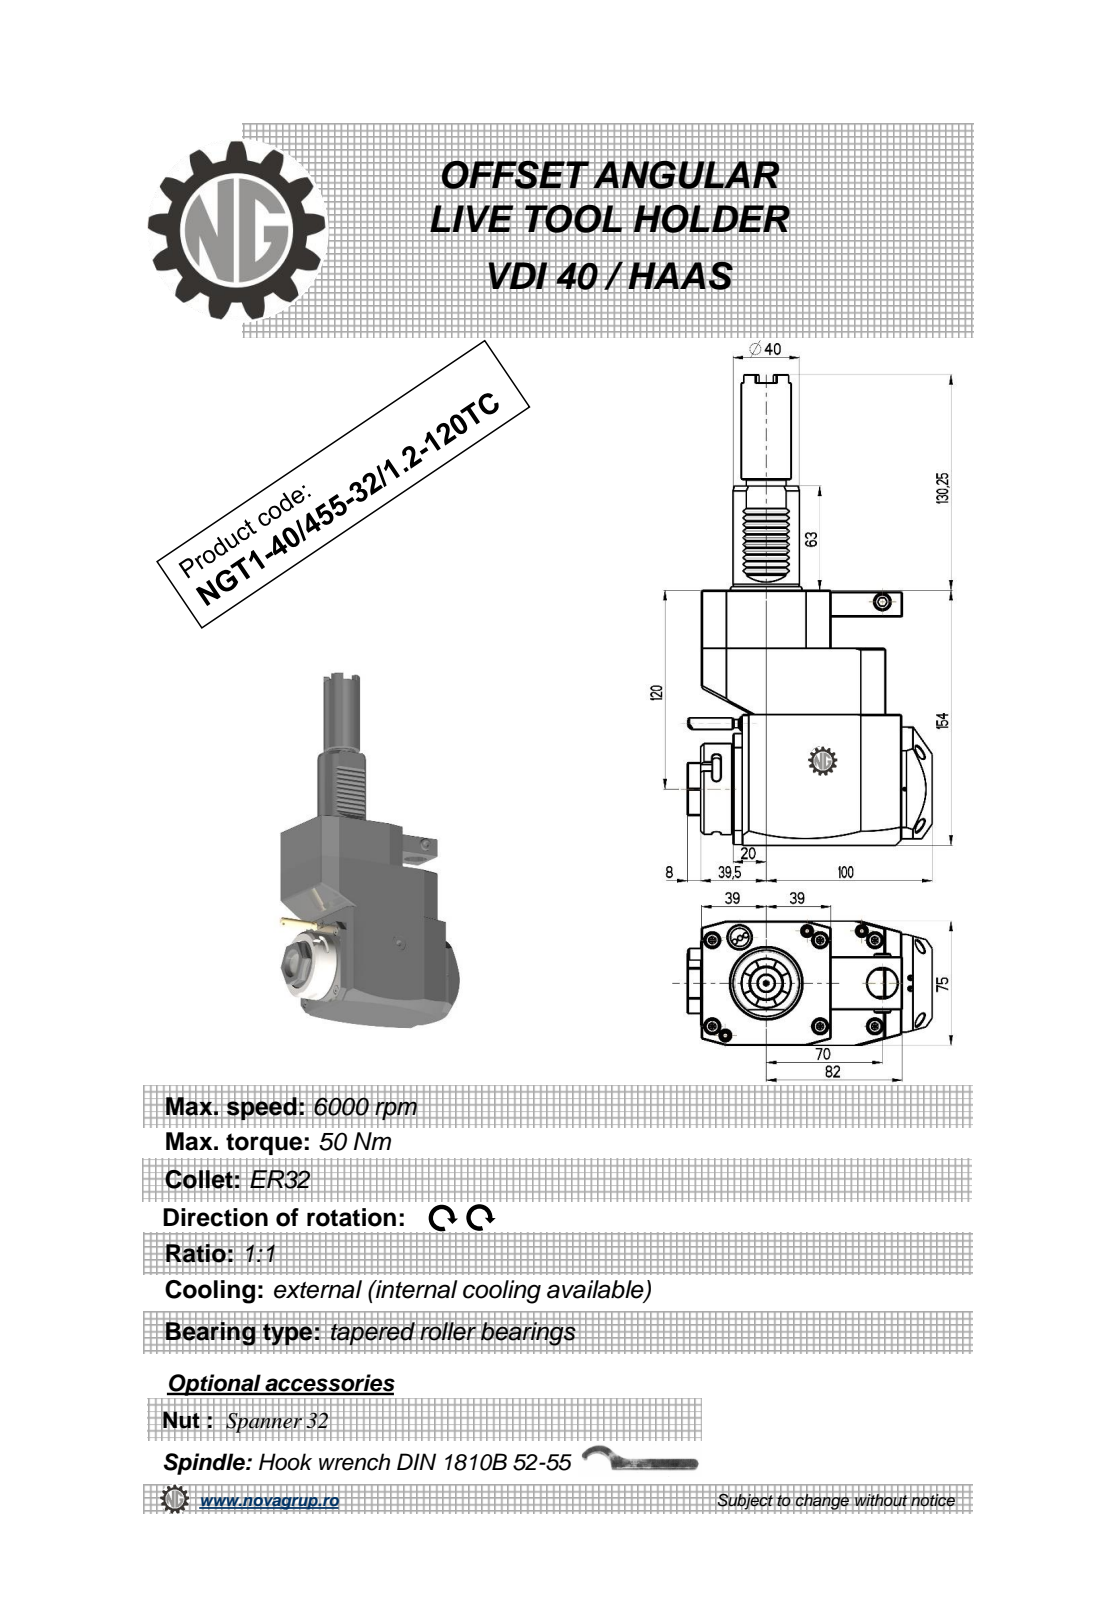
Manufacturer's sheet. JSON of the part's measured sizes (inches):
{"part_name": "NGT1_40_455_32_1_2_120TC", "step_written_by": "PRO/ENGINEER BY PARAMETRIC TECHNOLOGY CORPORATION, 2010280 (CONFIG_CONTROL_DESIGN)", "units": "inches", "bodies": {"solids": 1, "faces": 370, "planar": 222, "cylindrical": 64, "other": 84}, "overall_size": [11.191, 5.807, 2.953], "volume_in3": 80.55, "surface_area_in2": 152.2, "round_holes": [[0.098, 1], [0.118, 1], [0.374, 1], [0.709, 1], [0.787, 1], [0.906, 1]], "round_bosses_or_shafts": [[0.353, 2], [2.165, 1], [1.89, 1], [1.575, 1], [1.181, 1], [0.945, 1], [0.394, 1], [0.276, 1]], "partial_cylinders_radius": [[0.012, 10], [0.098, 6], [7.087, 2], [0.02, 1], [0.167, 1], [0.965, 1], [1.476, 1]], "face_to_face_distances": [2.953, 6.063, 0.748, 2.323, 0.02, 4.37, 3.622, 1.378, 4.685, 2.106], "hole_center_spacings": [1.701, 2.756, 2.956, 4.429]}
